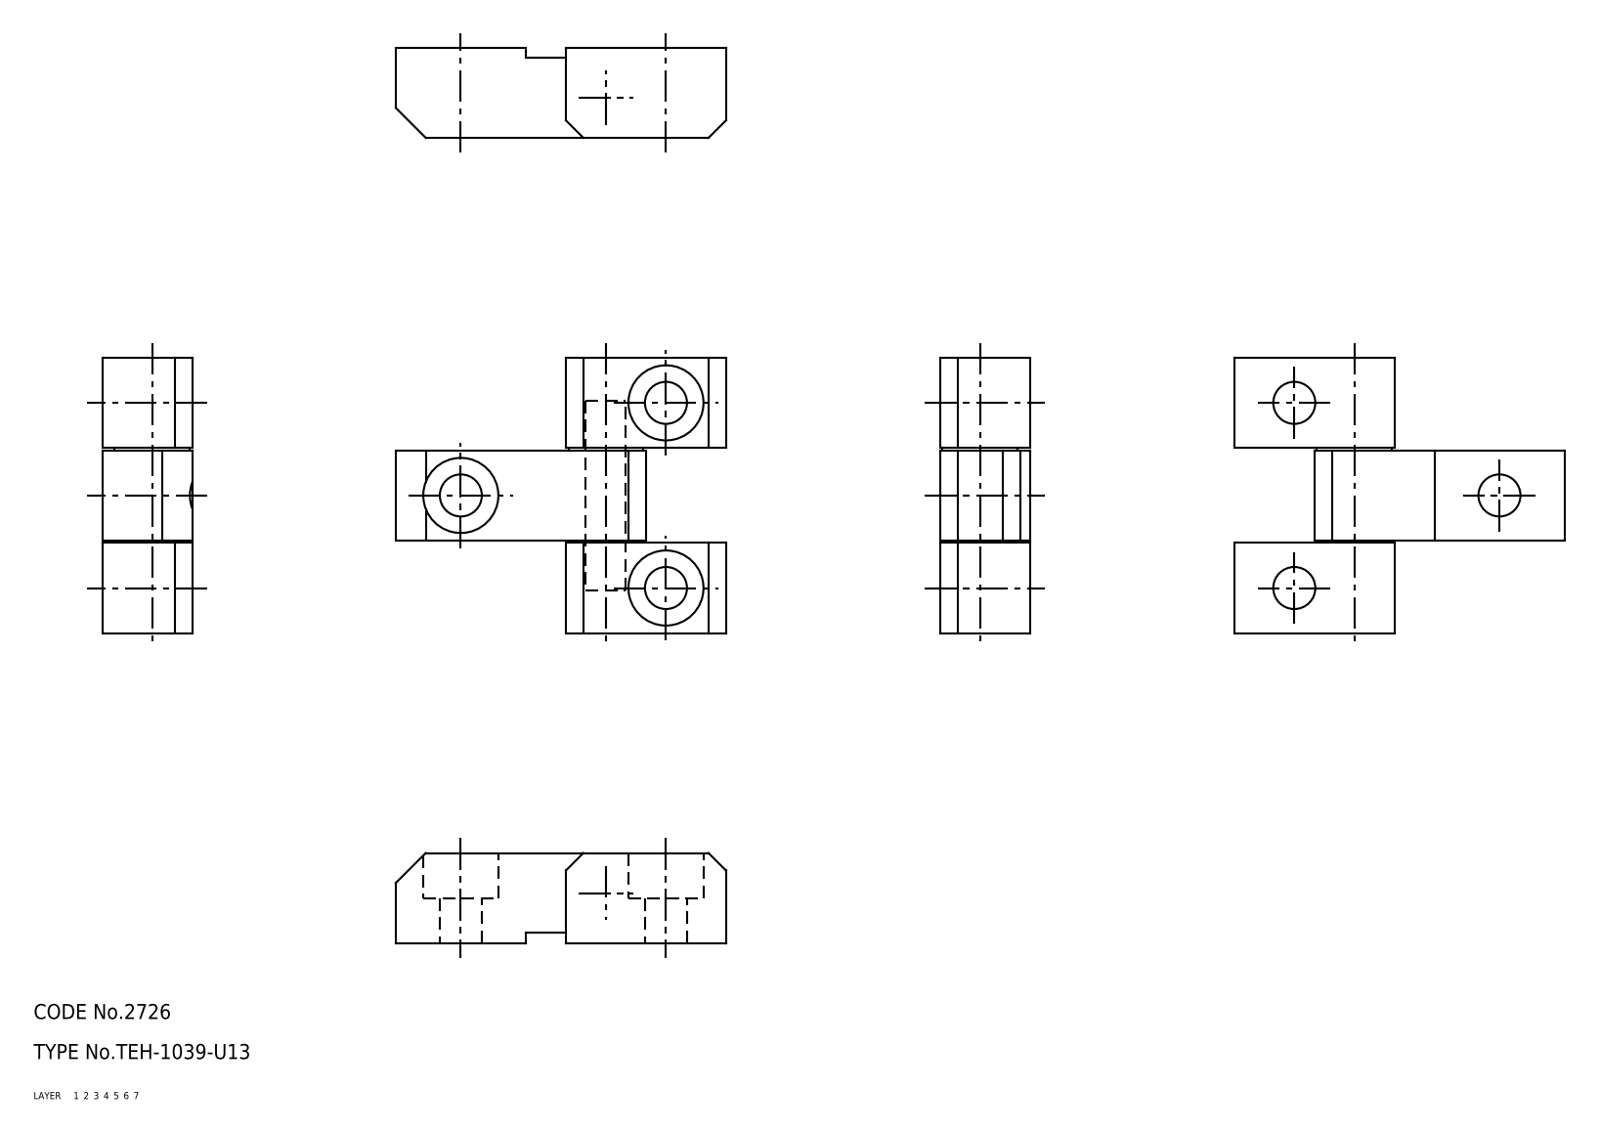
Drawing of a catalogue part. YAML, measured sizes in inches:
part_name: "hinge pieces_A_mr; washer; shaft; hinge pieces_B (+2 more)"
step_written_by: "CADfix (AUTOMOTIVE_DESIGN)"
units: inches
bodies: {solids: 6, faces: 66, planar: 0, cylindrical: 0, other: 66}
overall_size: [2.598, 2.165, 0.709]
volume: 1.75
surface_area: 21.53
